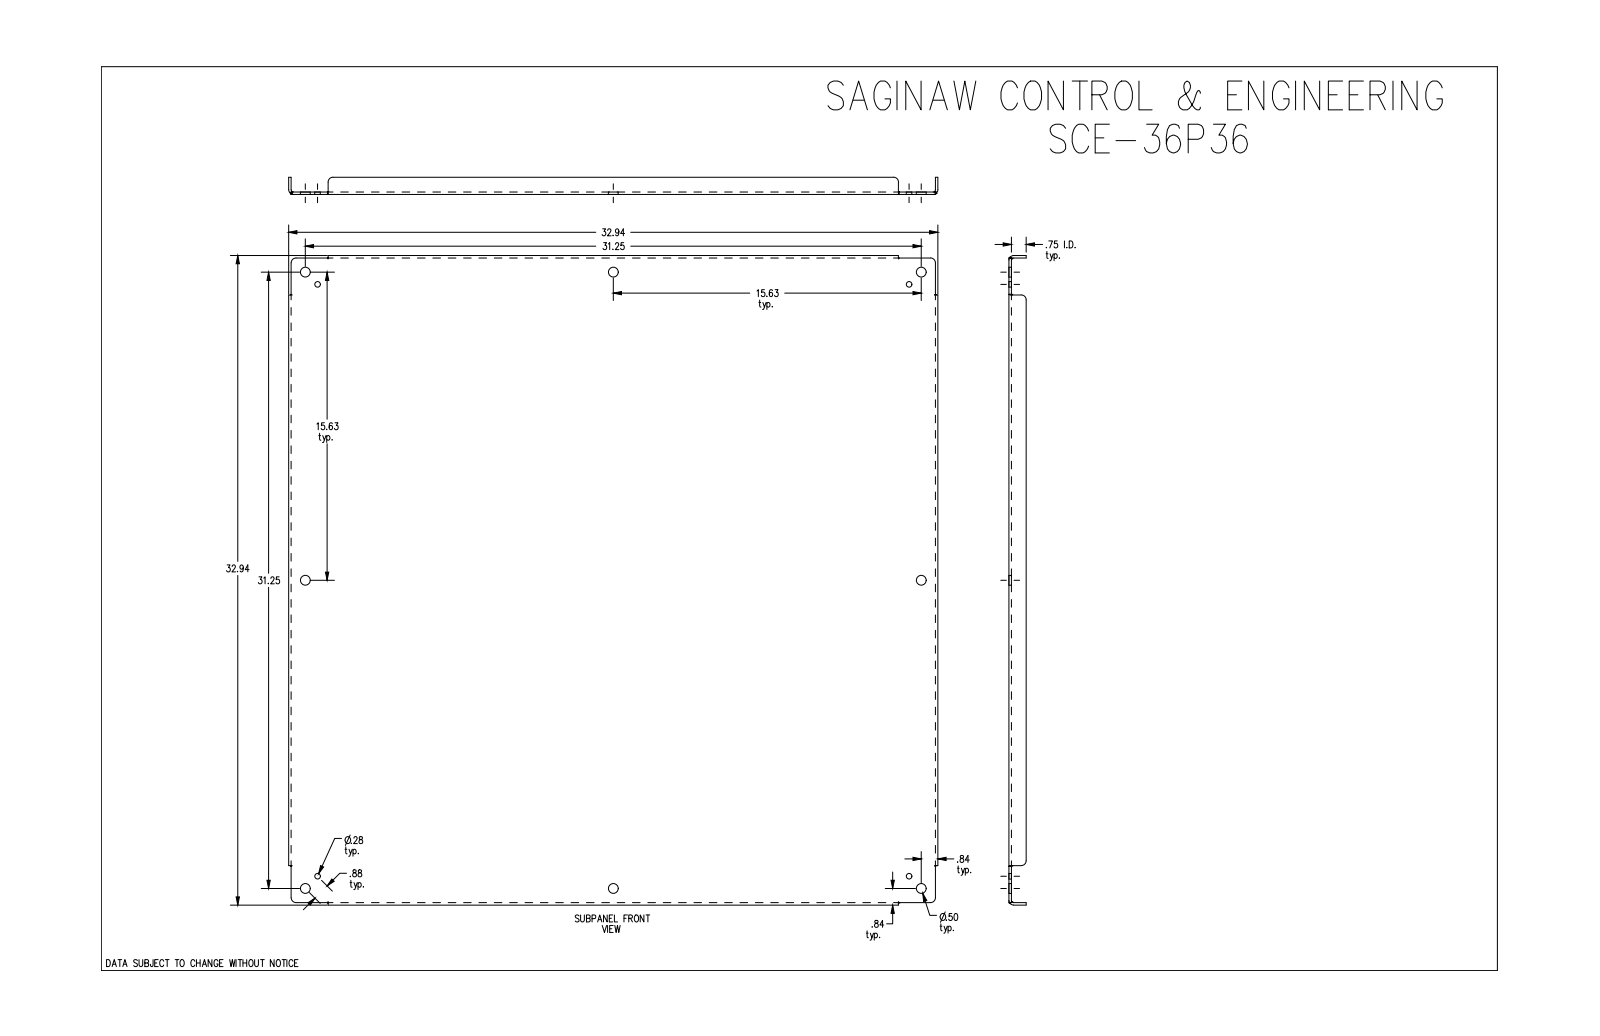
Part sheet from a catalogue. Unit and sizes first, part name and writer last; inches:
Units: inches
Overall size (bounding box): 32.938 × 32.938 × 0.875
Round holes (diameter × count): ⌀0.5 ×8, ⌀0.281 ×4
Partial cylindrical surfaces — rounded edges, fillets, slot ends (radius × count): R0.25 ×8, R0.112 ×4, R0.237 ×4
Main face-to-face distances: 0.125, 0.125, 32.813, 32.687, 32.938, 0.75, 0.875, 2, 30.938, 1.875
Hole centre spacings: 15.019, 15.625, 30.638, 34.11, 34.939, 31.25, 0.875, 22.097
Volume: 144.9 in³ · Surface area: 2 337 in²
Bodies: 1 solid, 86 faces (30 planar, 32 cylindrical, 24 other)
Part name (STEP PRODUCT): SCE-36P36
STEP written by: SolidWorks 2019 (CONFIG_CONTROL_DESIGN)
